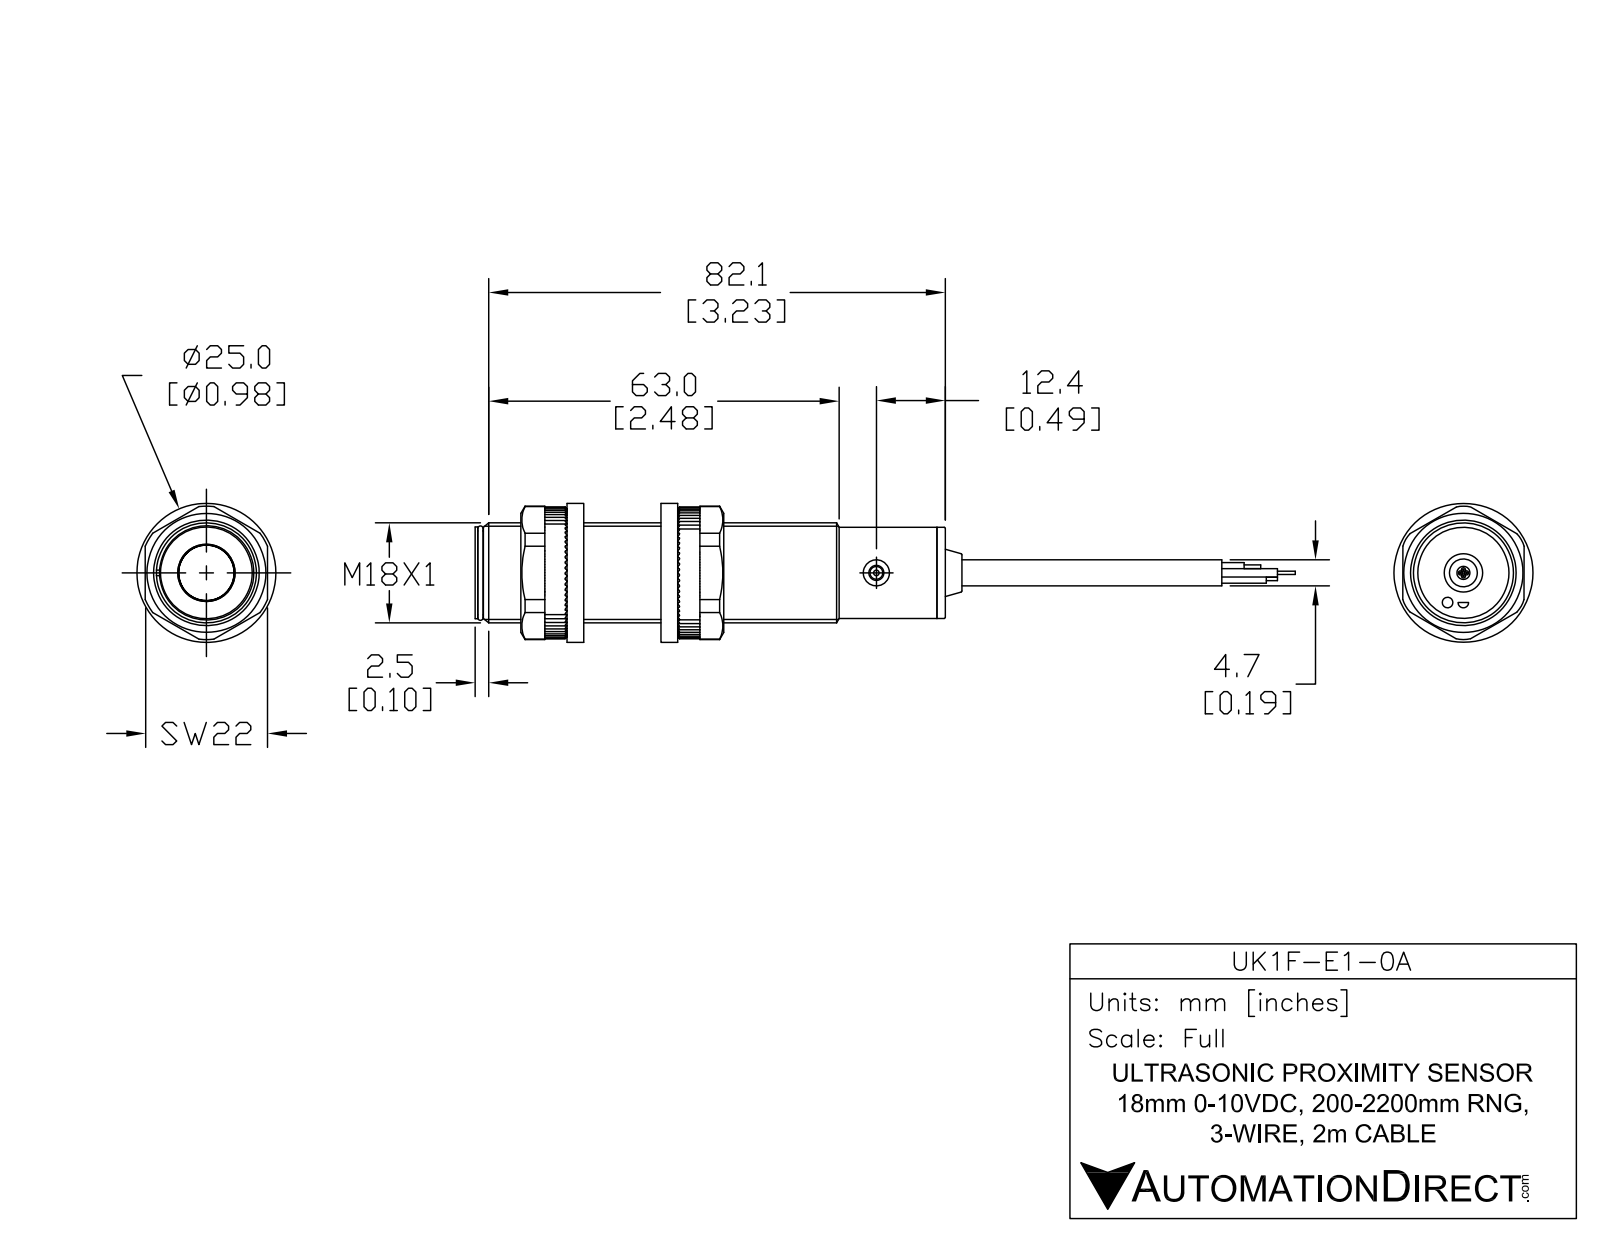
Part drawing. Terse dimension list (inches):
name: UK1F-E1-0A
written by: SolidWorks 2017 (AUTOMOTIVE_DESIGN)
unit: in
bodies: 6 solids, 55 faces (17 planar, 24 cylindrical, 14 other)
size: 4.832 × 0.709 × 0.709
volume: 1.285 in³; area: 10.69 in²
holes: 2× ⌀0.185, 1× ⌀0.106
bosses: 1× ⌀0.709, 1× ⌀0.646, 1× ⌀0.622, 1× ⌀0.374, 1× ⌀0.189, 1× ⌀0.091
face distances: 3.193, 3.252, 0.059, 0.039, 3.232, 3.291, 0.041, 3.234, 3.293, 3.257
